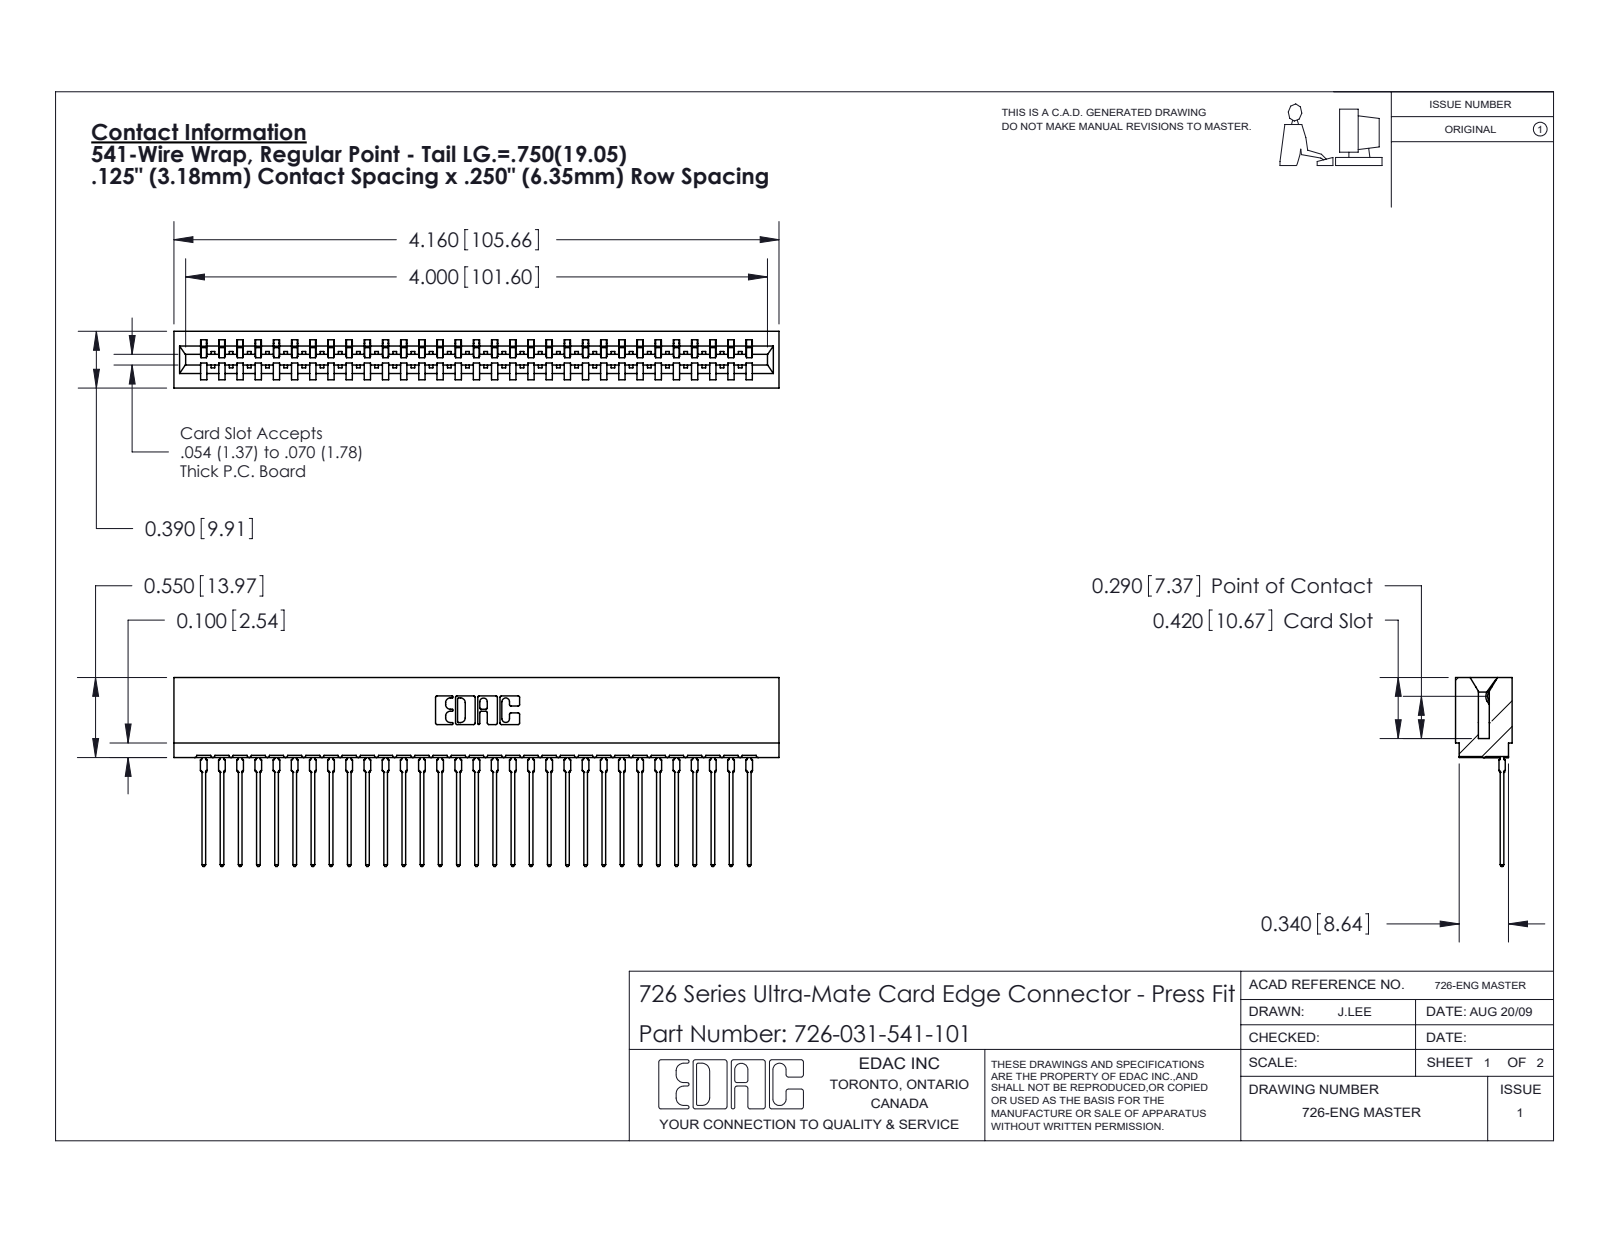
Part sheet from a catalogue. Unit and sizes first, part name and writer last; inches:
Units: inches
Overall size (bounding box): 4.16 × 1.299 × 0.39
Partial cylindrical surfaces — rounded edges, fillets, slot ends (radius × count): R0.021 ×62, R0.015 ×32, R0.01 ×22, R0.007 ×6, R0.031 ×6, R0.005 ×4, R0.011 ×4, R0.026 ×3
Main face-to-face distances: 0.057, 0.333, 0.25, 0.39, 0.025, 0.307, 0.083, 0.275, 1, 0.365
Volume: 0.589 in³ · Surface area: 23.71 in²
Bodies: 32 solids, 3445 faces (2008 planar, 631 cylindrical, 806 other)
Part name (STEP PRODUCT): 726 Part_.515 Slot Depth - 01; 746-292-001_541; 726-031-541-101
STEP written by: SolidWorks 2020 (CONFIG_CONTROL_DESIGN)
